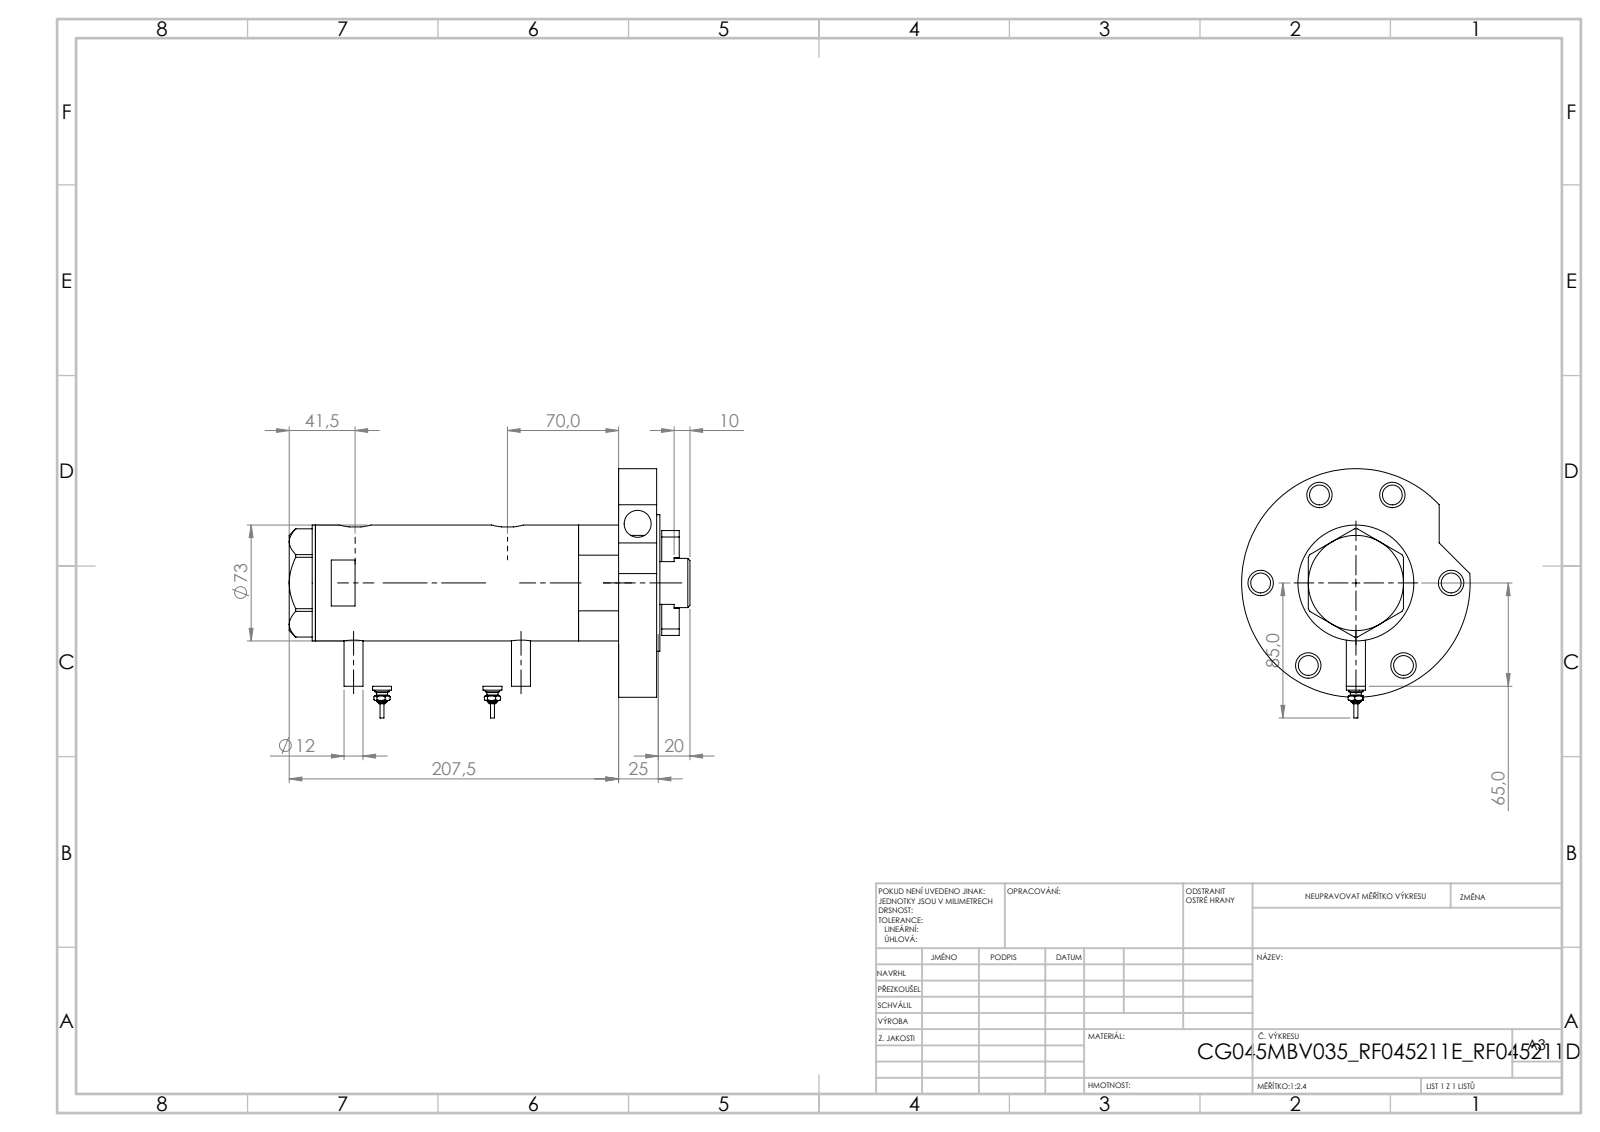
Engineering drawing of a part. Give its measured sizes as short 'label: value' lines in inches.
name: V270CG_RF211E; V270CG_SWITCH; V270CG_MIDDLE; V270CG_FRONT (+3 more)
written by: SolidWorks 2019 (CONFIG_CONTROL_DESIGN)
unit: in
bodies: 9 solids, 315 faces (113 planar, 128 cylindrical, 74 other)
size: 8.918 × 5.669 × 5.669
volume: 65.3 in³; area: 304.9 in²
holes: 8× ⌀0.492, 6× ⌀0.63, 4× ⌀0.319, 4× ⌀0.531, 2× ⌀0.197, 2× ⌀0.518, 1× ⌀0.413, 1× ⌀0.669, 1× ⌀1.26, 1× ⌀1.319, 1× ⌀1.772, 1× ⌀1.89
bosses: 2× ⌀0.472, 2× ⌀0.354, 2× ⌀0.276, 2× ⌀0.197, 2× ⌀0.171, 2× ⌀0.094, 1× ⌀5.669, 1× ⌀3.386
rounds: 2× R0.394
face distances: 0.945, 6.395, 1.024, 7.34, 0.079, 7.419, 2.998, 0.65, 7.045, 7.99
hole spacings: 2.362, 0.99, 2.272, 2.82, 0.591, 1.38, 1.413, 1.724
